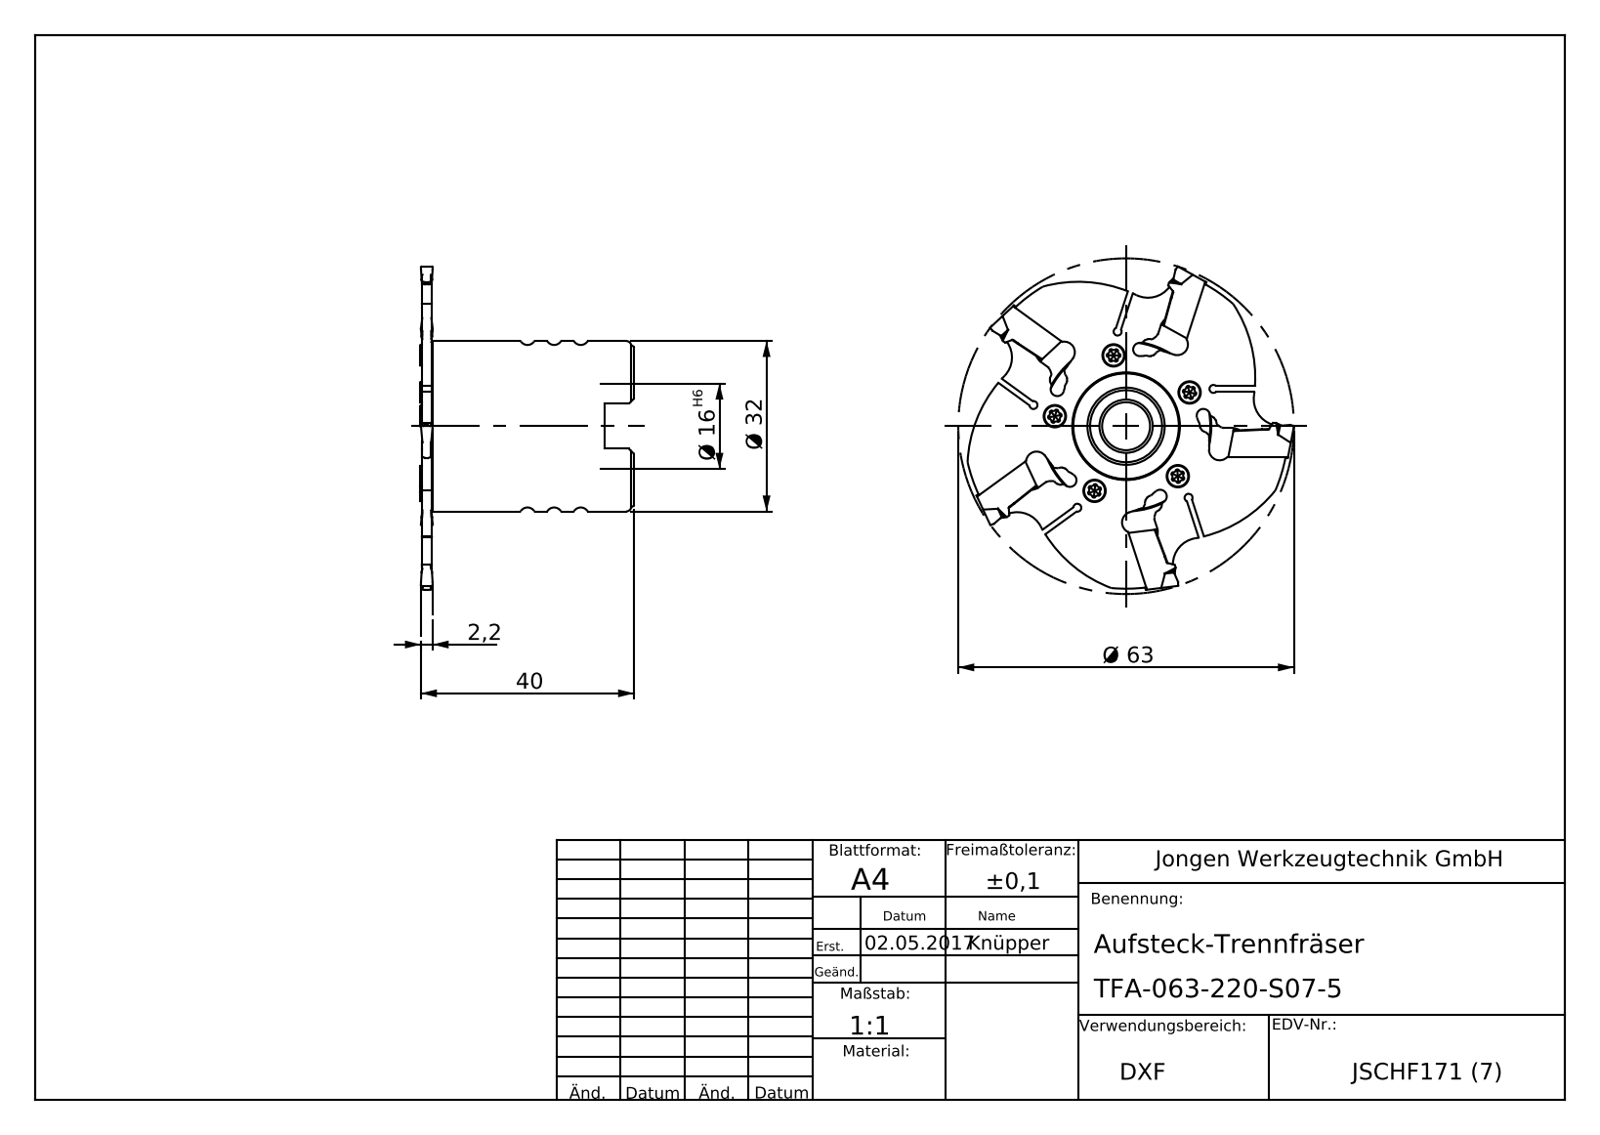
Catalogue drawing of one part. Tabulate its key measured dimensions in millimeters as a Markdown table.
| quantity | value |
| --- | --- |
| part name | TFA-063-220-S07-5 |
| STEP written by | SolidWorks 2018 (AUTOMOTIVE_DESIGN) |
| units | millimeters |
| bodies | 1 solid, 113 faces (19 planar, 80 cylindrical, 14 other) |
| overall size | 63 × 63 × 2.2 |
| volume | 5 652 mm³ |
| surface area | 6 210 mm² |
| round holes (diameter × count) | 3.2 × 5, 4.2 × 5, 20 × 1, 33.69 × 1 |
| round bosses / shafts (diameter × count) | 63 × 1 |
| partial cylindrical surfaces (radius × count) | 1 × 20, 2 × 10, 1.25 × 5, 4.64 × 5, 7.14 × 5 |
| main face-to-face distances | 2.2, 1.95, 1.7, 3.2, 3.19 |
| hole center spacings | 13.5, 15.87, 25.68, 25.67, 13.49, 15.86 |
